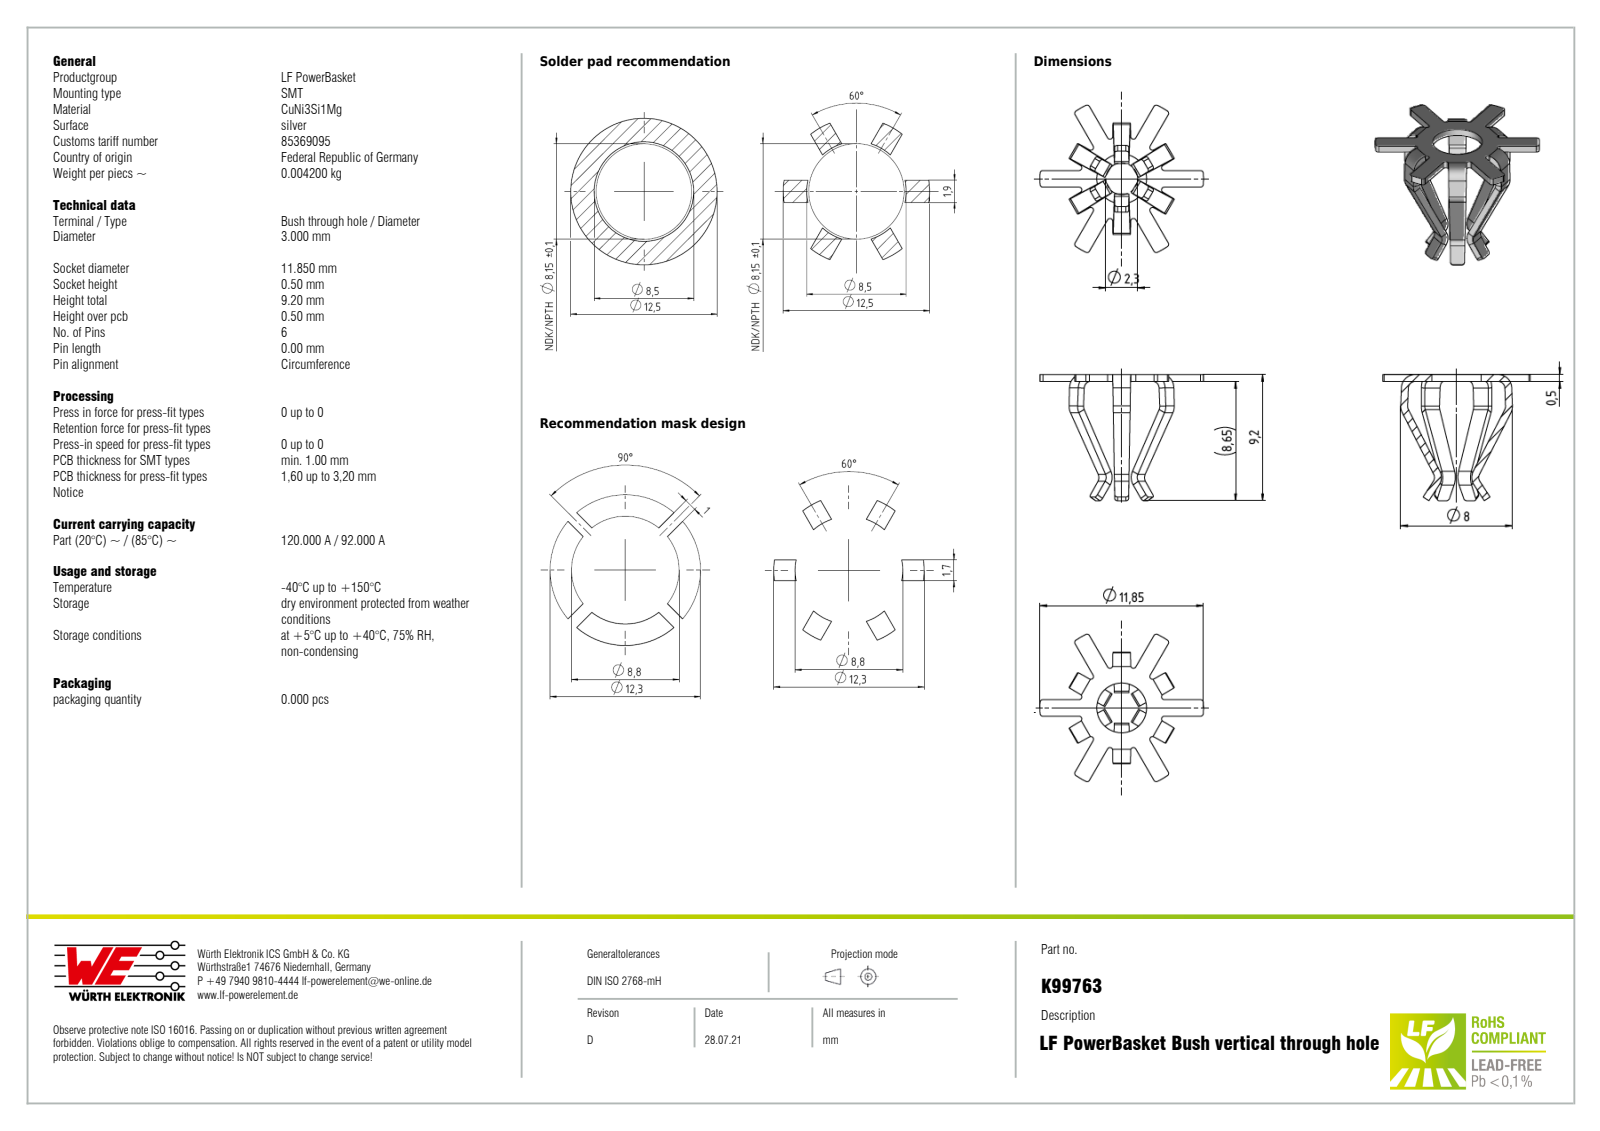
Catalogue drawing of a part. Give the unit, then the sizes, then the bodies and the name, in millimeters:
Units: millimetres
Overall size (bounding box): 11.85 × 10.69 × 9.15
Round holes (diameter × count): ⌀3.61 ×1
Partial cylindrical surfaces — rounded edges, fillets, slot ends (radius × count): R0.2 ×36, R0.5 ×18, R1 ×18, R5.92 ×1
Main face-to-face distances: 0.5, 1.2
Volume: 54 mm³ · Surface area: 308 mm²
Bodies: 1 solid, 229 faces (92 planar, 89 cylindrical, 48 other)
Part name (STEP PRODUCT): K99763-D
STEP written by: SolidWorks 2018 (AUTOMOTIVE_DESIGN)
